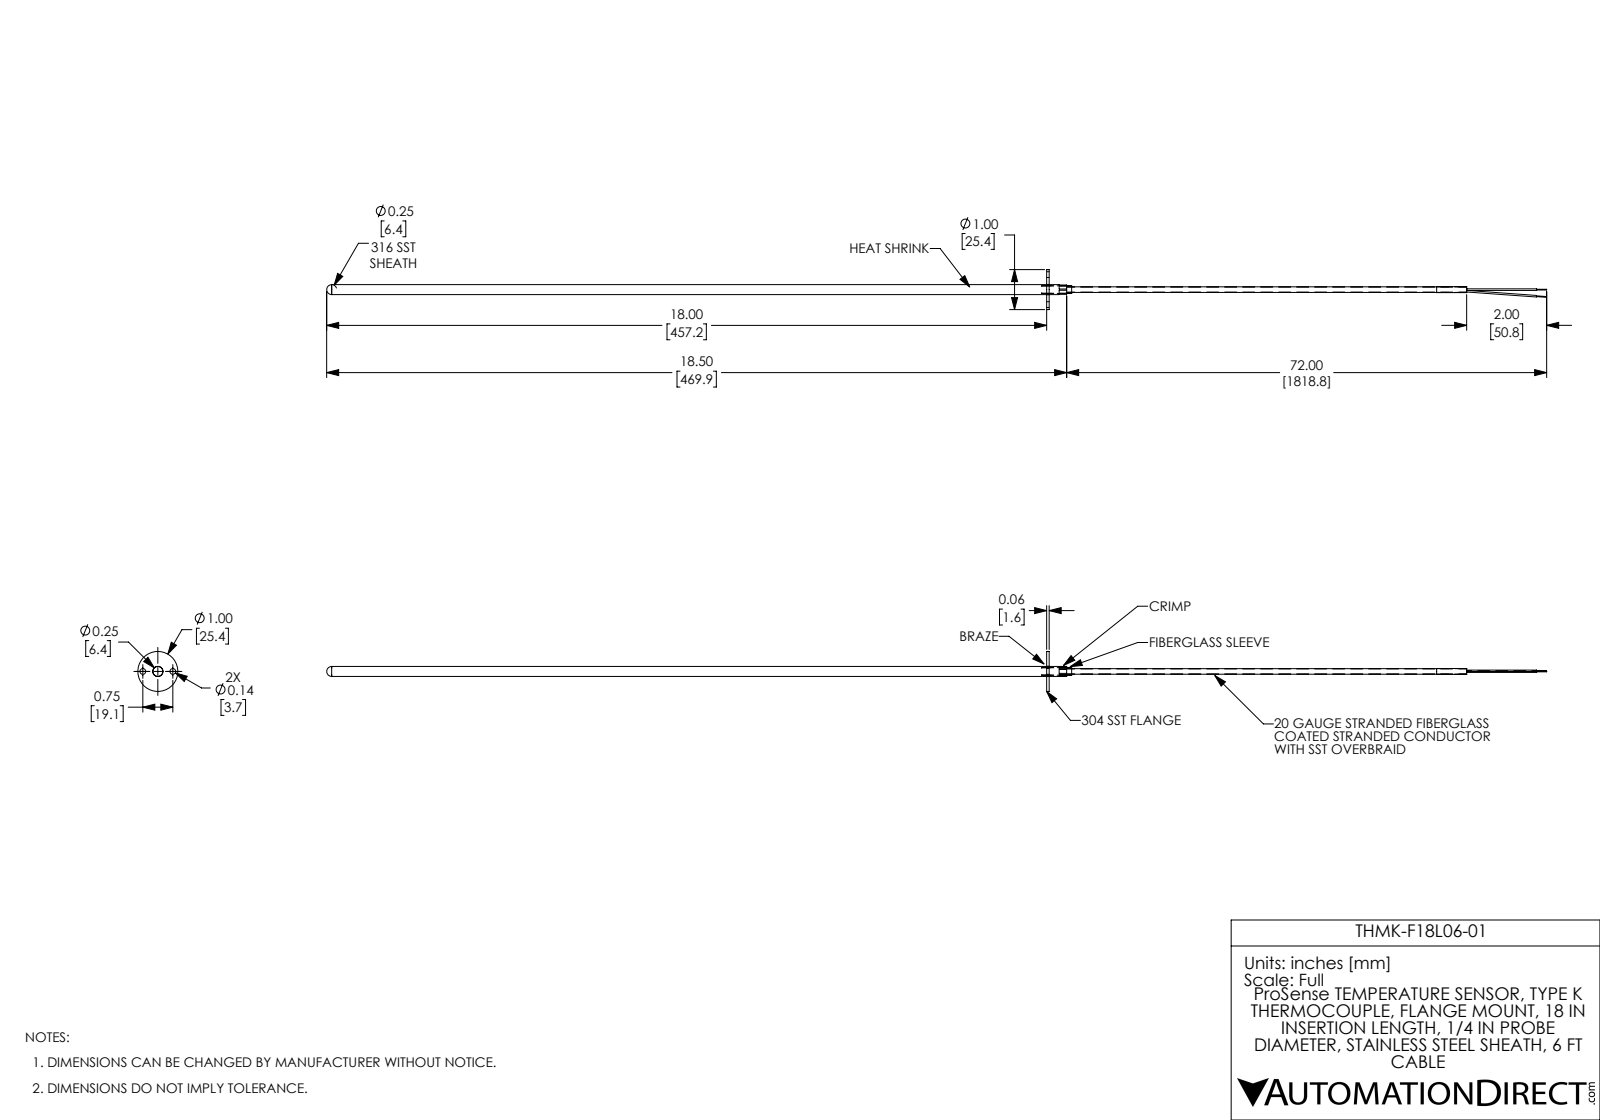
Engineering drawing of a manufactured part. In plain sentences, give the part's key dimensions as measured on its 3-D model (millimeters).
The part is named "THMJ-F18L06-02". Its 3-D file was written by "SolidWorks 2017 (AUTOMOTIVE_DESIGN)". It is 7 solids with 65 faces: 30 planar, 32 cylindrical and 3 other. Overall it measures 774.7 by 25.4 by 25.4 millimeters. Its volume is 18 370 cubic millimeters and its surface area 20 440 square millimeters. Round holes: 3 of diameter 3.7, 1 of diameter 3.5, 1 of diameter 4.8, 1 of diameter 6.5. Round bosses or shafts: 1 of diameter 25.4, 1 of diameter 6.4, 1 of diameter 4.8, 1 of diameter 4.8, 1 of diameter 3.8, 1 of diameter 3.6, 1 of diameter 3.4, 1 of diameter 1. The main face-to-face distances are 1.6, 12.7, 11.1, 5.9, 19.1, 3.2, 4.8, 15.9, 15.9, 14.3. The hole center spacings are 9.5, 9.5, 19.1.
